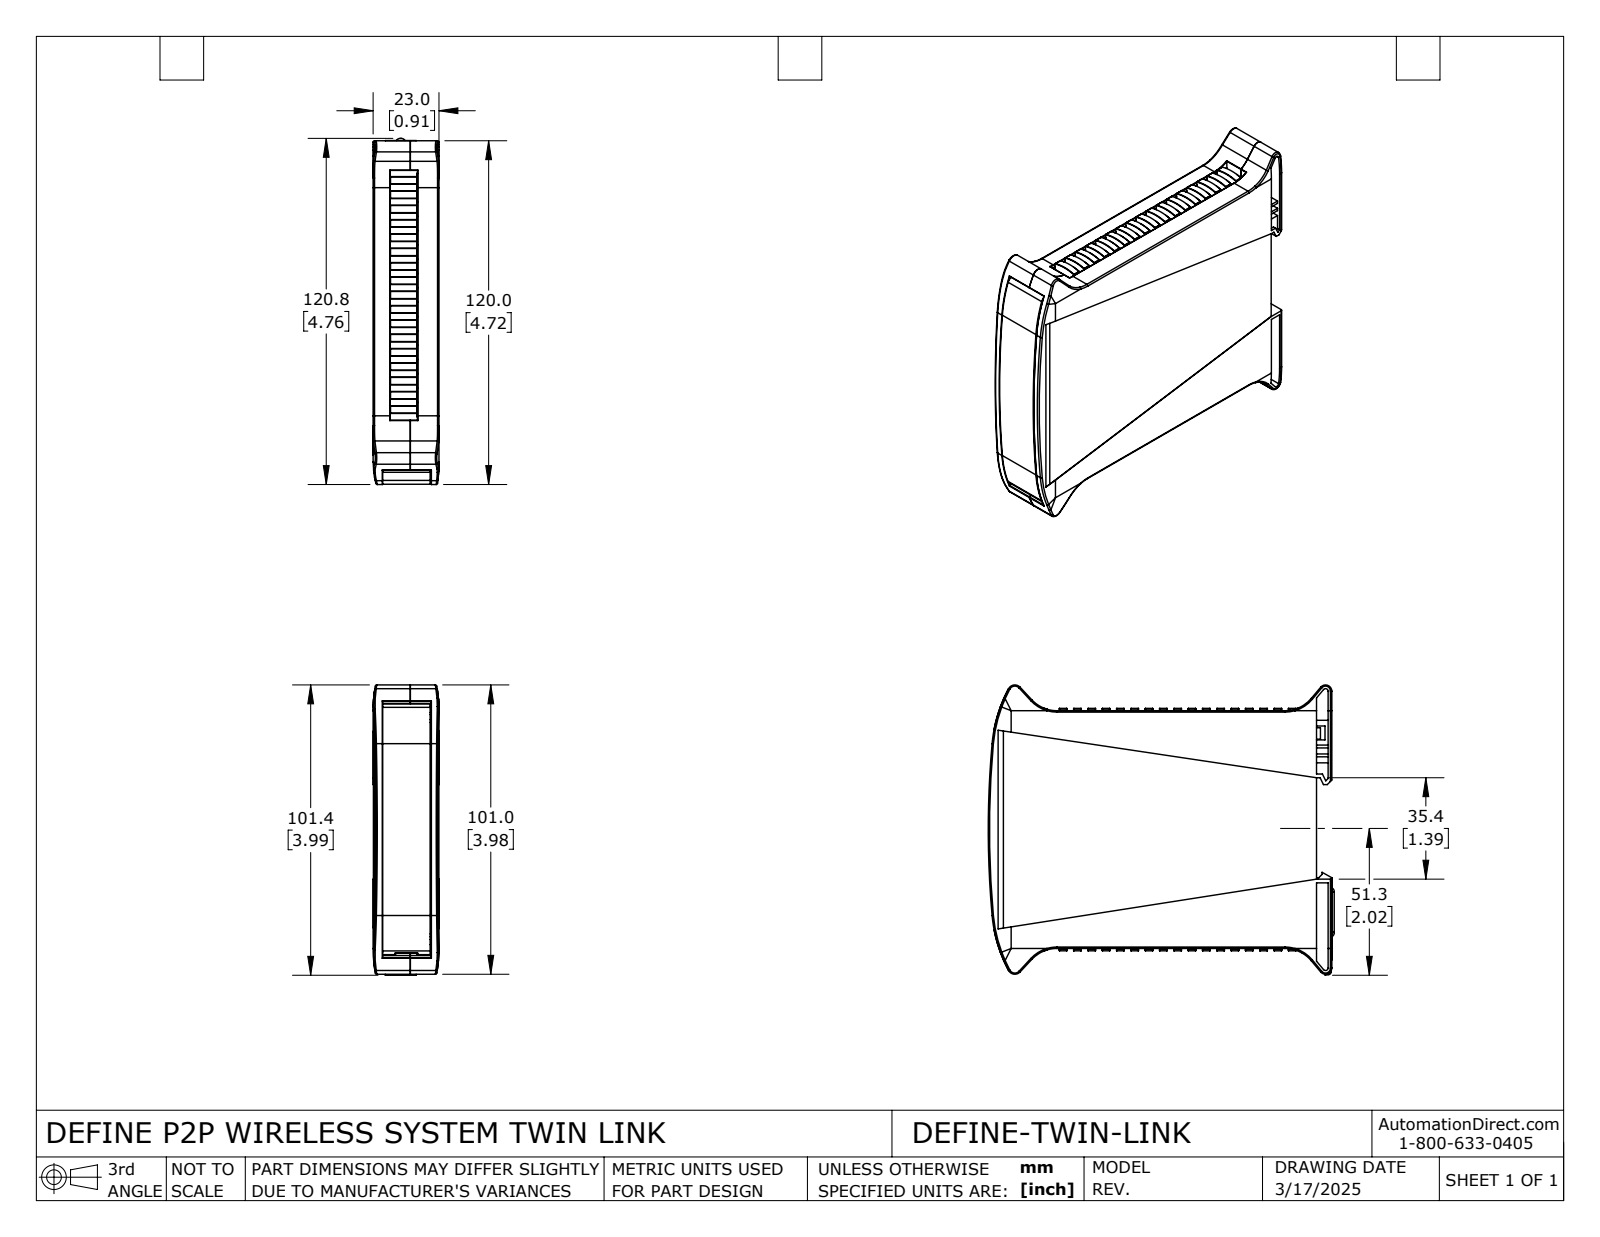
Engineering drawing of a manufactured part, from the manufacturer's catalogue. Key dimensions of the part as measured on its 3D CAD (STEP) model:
Part name (STEP PRODUCT): DEFINE-TWIN-LINK
STEP written by: SolidWorks 2024 (AUTOMOTIVE_DESIGN)
Units: inches
Bodies: 7 solids, 1721 faces (1207 planar, 332 cylindrical, 182 other)
Overall size (bounding box): 4.757 × 3.99 × 0.906
Volume: 3.092 in³ · Surface area: 111.6 in²
Round holes (diameter × count): ⌀0.118 ×4, ⌀0.075 ×1, ⌀0.146 ×1, ⌀0.241 ×1
Round bosses / shafts (diameter × count): ⌀0.089 ×1
Partial cylindrical surfaces — rounded edges, fillets, slot ends (radius × count): R0.01 ×15, R0.02 ×11, R0.006 ×10, R0.004 ×4, R0.039 ×4, R0.472 ×4, R1.893 ×4, R0.079 ×3
Main face-to-face distances: 0.778, 0.055, 0.902, 0.065, 0.833, 0.898, 0.843, 0.069, 0.059, 0.837
Hole centre spacings: 4.058, 5.368, 0.268, 0.739, 3.268, 3.546, 3.78, 4.175
